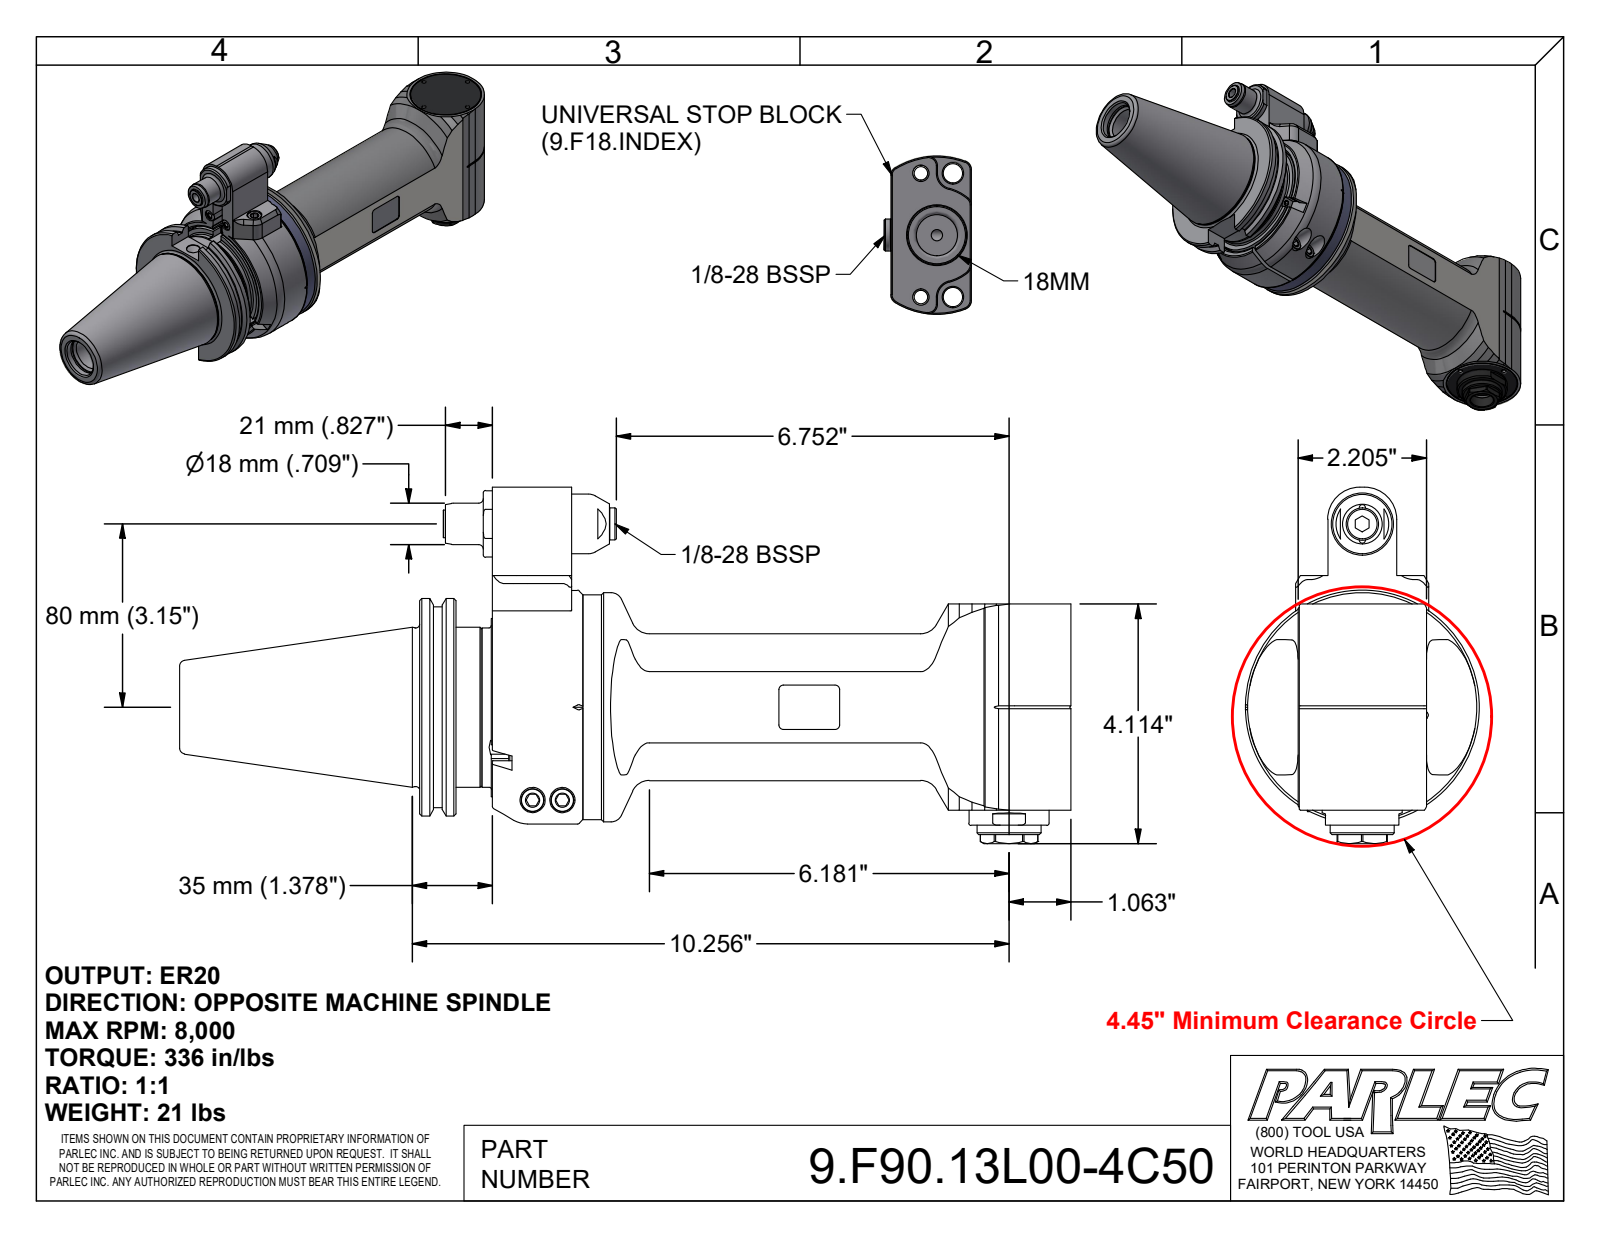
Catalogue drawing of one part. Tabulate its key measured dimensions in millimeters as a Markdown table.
| quantity | value |
| --- | --- |
| part name | 9.F90.13L00-4C50; 9.F90.13L00; 9GA11C_458 (EVO, Type 1, Cat50, 80mm) |
| STEP written by | Autodesk Inventor 2022 (AUTOMOTIVE_DESIGN) |
| units | millimeters |
| bodies | 4 solids, 596 faces (266 planar, 158 cylindrical, 172 other) |
| overall size | 389.1 × 155.5 × 102 |
| volume | 1 557 000 mm³ |
| surface area | 181 500 mm² |
| round holes (diameter × count) | 3.2 × 4, 6.5 × 3, 2.6 × 2, 3.3 × 2, 4.2 × 2, 5 × 2, 8 × 2, 10.4 × 2, 11 × 2, 12.5 × 2, 29 × 2, 2.5 × 1 |
| round bosses / shafts (diameter × count) | 10 × 4, 18 × 2, 12 × 2, 8 × 2, 6 × 2, 2.5 × 2, 102 × 1, 100 × 1 |
| partial cylindrical surfaces (radius × count) | 1 × 14, 2 × 12, 3 × 6, 4 × 4, 0.4 × 2, 0.5 × 2, 8 × 2, 14 × 2 |
| main face-to-face distances | 56, 32.5, 0.5, 32, 1, 55.4, 23.4, 23, 71.3, 39.3 |
| hole center spacings | 21.5, 30.4, 7, 21.5, 24.4, 31, 37.8, 43 |
